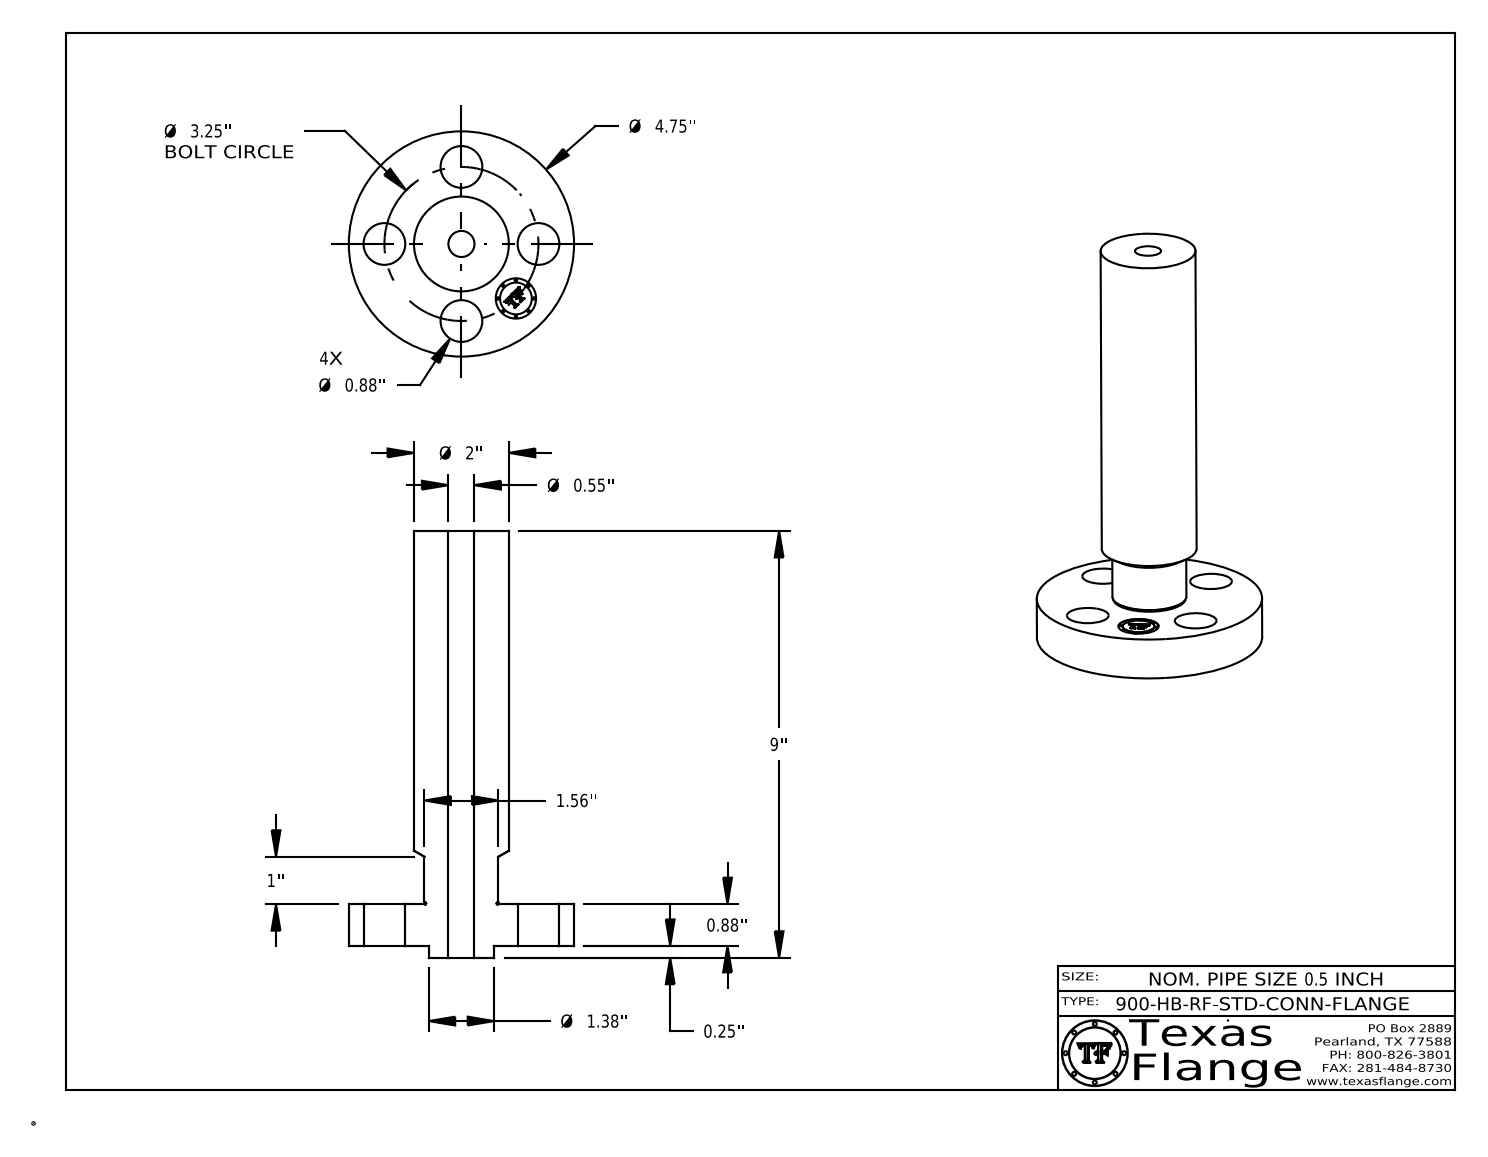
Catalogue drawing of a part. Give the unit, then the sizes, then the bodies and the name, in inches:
Units: inches
Overall size (bounding box): 9 × 4.75 × 4.75
Round holes (diameter × count): ⌀0.88 ×4, ⌀0.55 ×1, ⌀0.85 ×1
Round bosses / shafts (diameter × count): ⌀0.051 ×8, ⌀4.75 ×1, ⌀2 ×1, ⌀1.56 ×1, ⌀1.38 ×1, ⌀0.67 ×1
Main face-to-face distances: 0.88, 8.75, 7.87, 0.25, 1.13, 9, 1.125, 0.875, 7.875, 0.254
Hole centre spacings: 1.625, 2.298, 1.244, 3.003, 3.25
Volume: 35.1 in³ · Surface area: 119.8 in²
Bodies: 1 solid, 413 faces (369 planar, 38 cylindrical, 6 other)
Part name (STEP PRODUCT): 0.5-900-HB-RF-STD-CONN-FLANGE
STEP written by: CATIA V5 STEP AP214 (AUTOMOTIVE_DESIGN)
